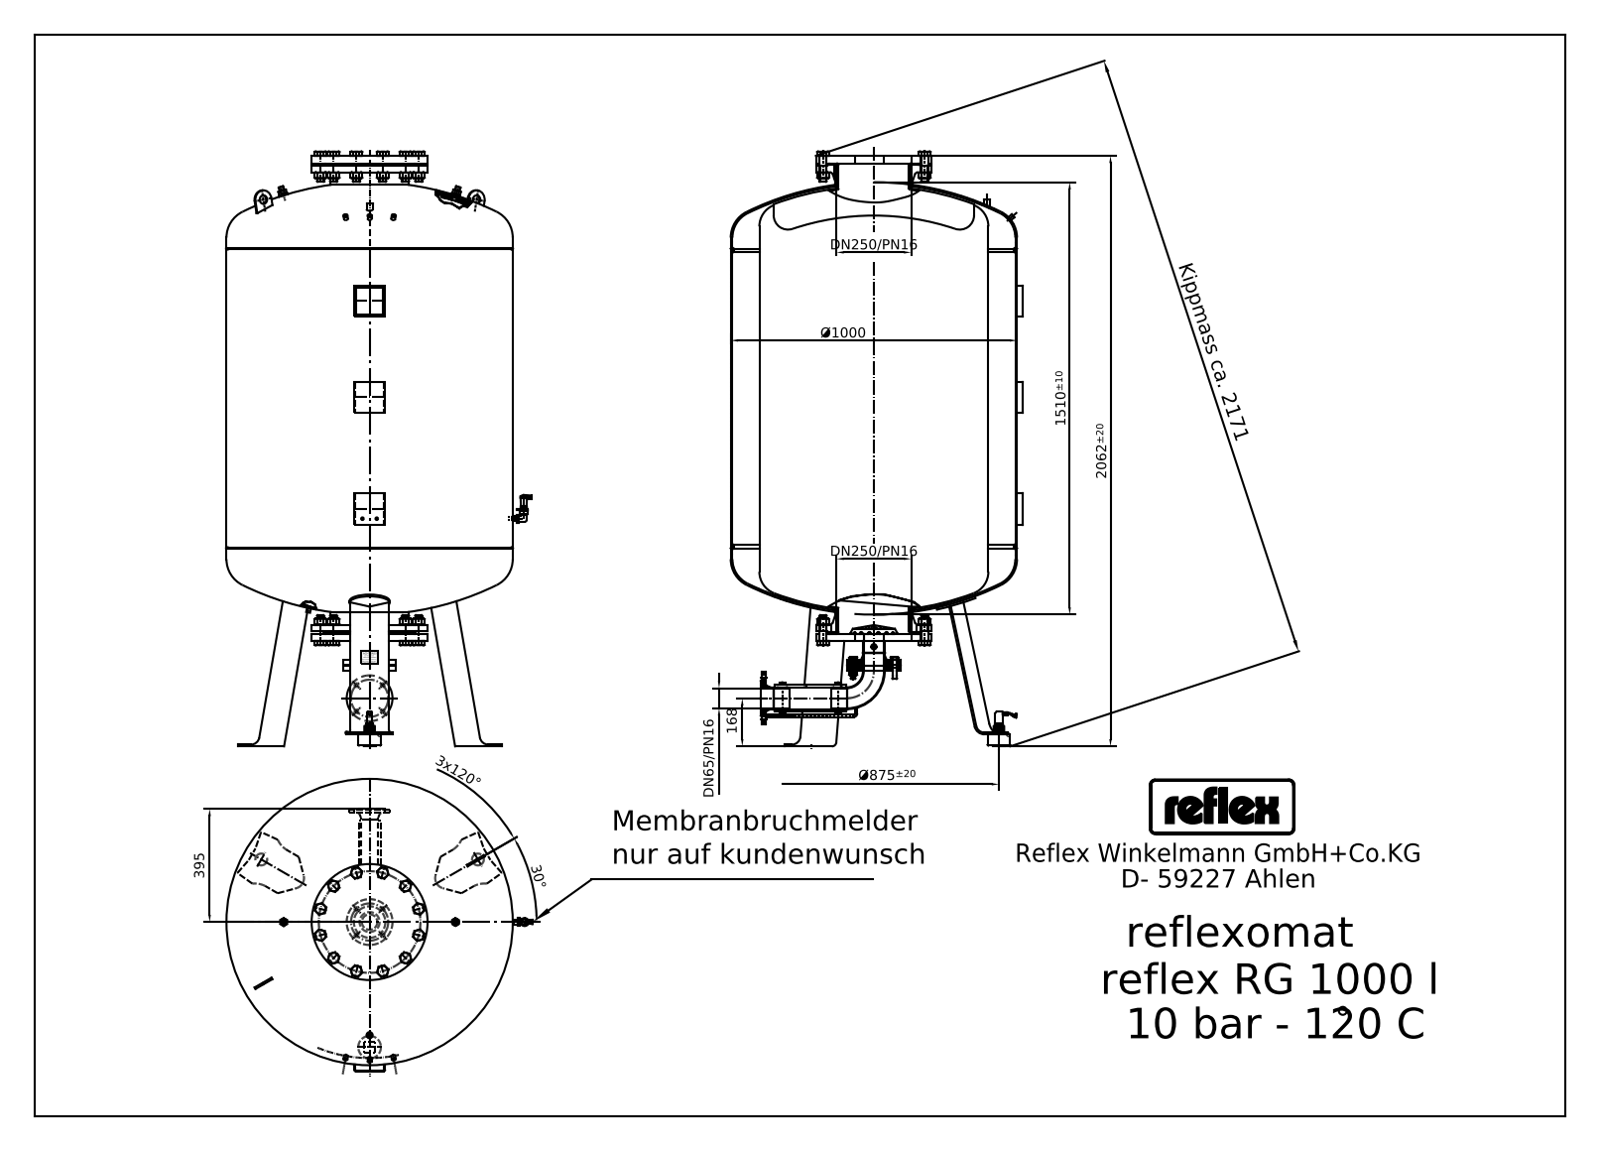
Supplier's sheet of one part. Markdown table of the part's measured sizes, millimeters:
| quantity | value |
| --- | --- |
| STEP written by | Mechanical Desktop 2009 (CONFIG_CONTROL_DESIGN) |
| units | millimeters |
| bodies | 33 solids, 1189 faces (675 planar, 280 cylindrical, 234 other) |
| overall size | 2060 × 1066 × 1020 |
| volume | 1 095 000 000 mm³ |
| surface area | 11 000 000 mm² |
| round holes (diameter × count) | 9 × 2, 11.45 × 2, 3.5 × 1, 8 × 1, 14.95 × 1, 30 × 1, 260.4 × 1 |
| round bosses / shafts (diameter × count) | 16 × 12, 12 × 4, 21.3 × 3, 18.5 × 3, 76.1 × 2, 28 × 2, 20 × 2, 10 × 2 |
| partial cylindrical surfaces (radius × count) | 25 × 18, 2 × 10, 1 × 5, 8.44 × 4, 3.38 × 3, 6 × 3, 3 × 2, 5.76 × 2 |
| main face-to-face distances | 1075, 22, 1645, 27, 1618, 1350.5, 275.5, 1372.5, 297.5, 294.5 |
| hole center spacings | 681.46, 50, 395, 519.5, 652.61 |
